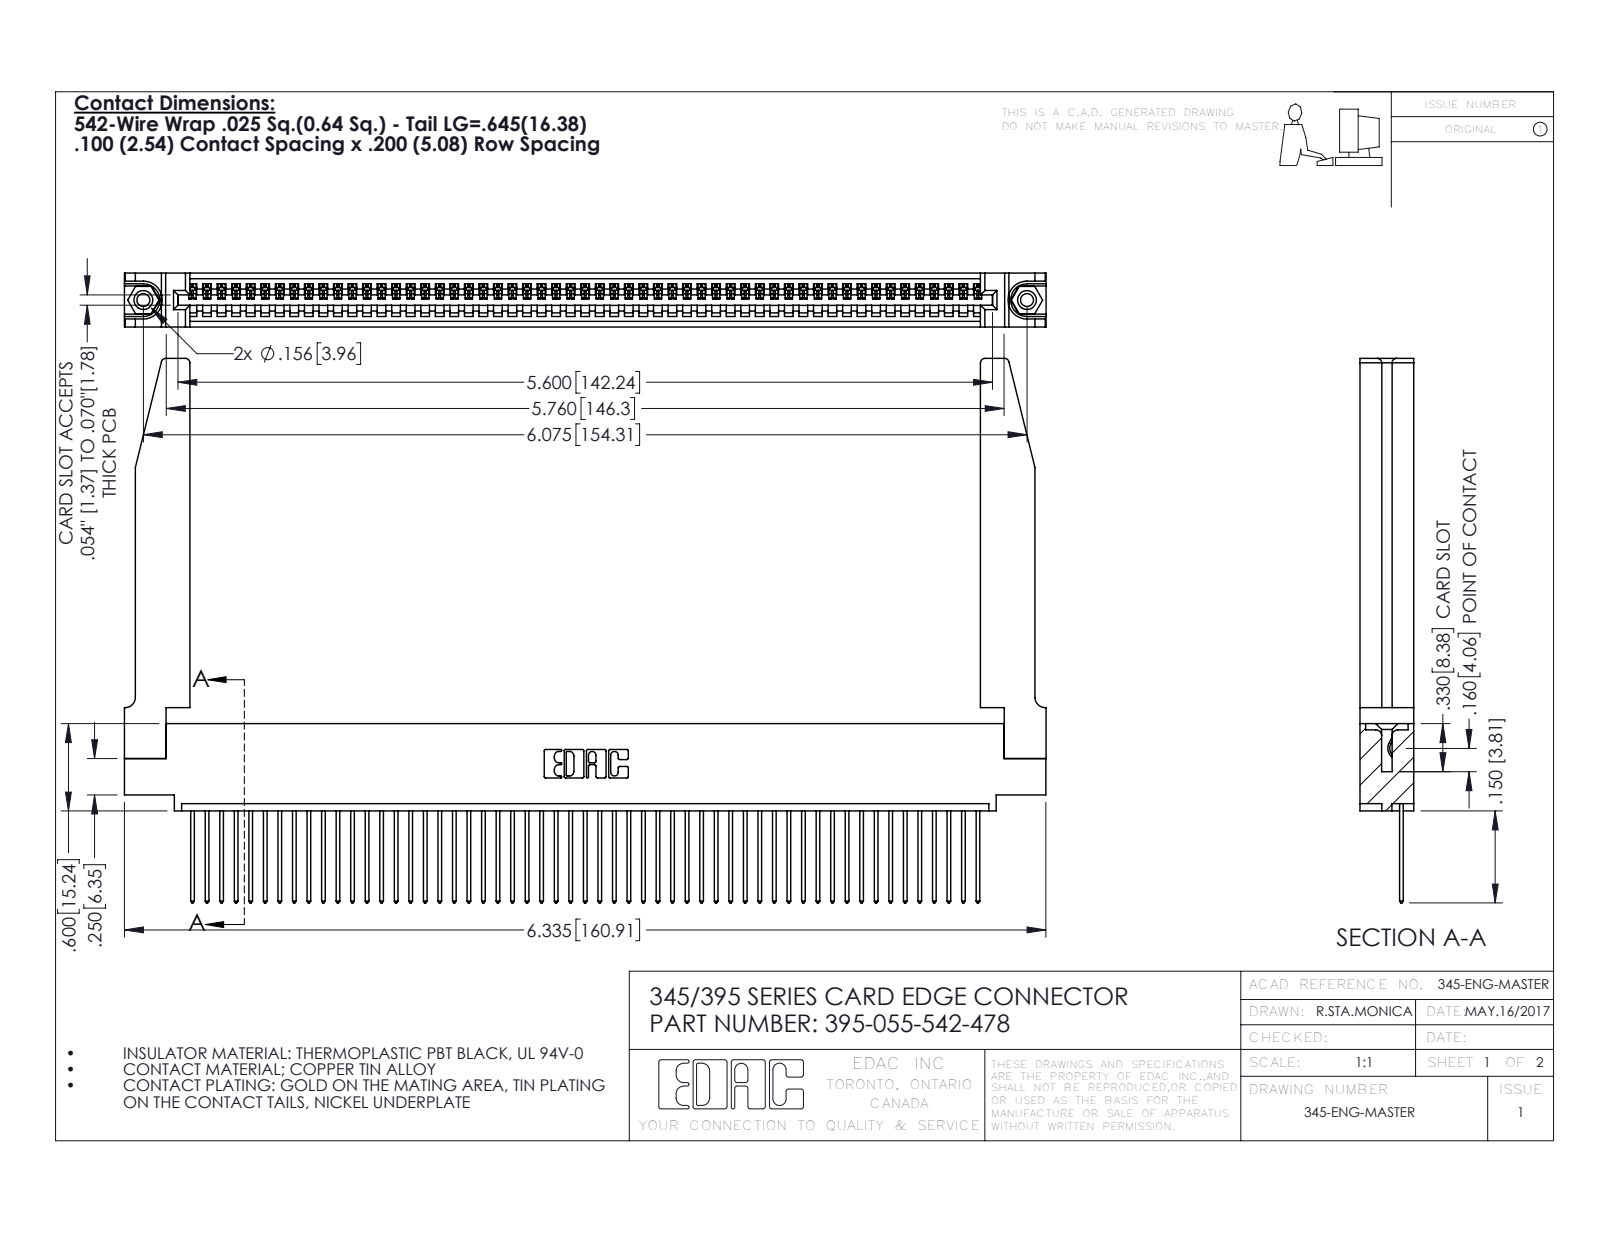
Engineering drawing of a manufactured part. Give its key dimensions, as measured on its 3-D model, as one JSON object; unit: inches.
{"part_name": "345-220-078_345-220-078; 345-250-001_345-250-001-102; 345-292-001_345-293-142; 345 Part_0.110 Offset - 0.156 Dia-TH (+1 more)", "step_written_by": "SolidWorks 2016 (CONFIG_CONTROL_DESIGN)", "units": "inches", "bodies": {"solids": 60, "faces": 3554, "planar": 2426, "cylindrical": 1076, "other": 52}, "overall_size": [6.336, 3.742, 0.37], "volume_in3": 1.416, "surface_area_in2": 44.02, "round_holes": [[0.089, 2], [0.125, 2], [0.156, 2], [0.064, 1]], "round_bosses_or_shafts": [[0.155, 2]], "partial_cylinders_radius": [[0.006, 110], [0.01, 110], [0.01, 22], [0.03, 8], [0.007, 6], [0.031, 6], [0.026, 3], [0.031, 2]], "face_to_face_distances": [0.072, 0.298, 0.37, 0.098, 0.272, 0.025, 0.2, 0.225, 0.148, 0.15], "hole_center_spacings": [0.27, 5.839, 6.075]}
